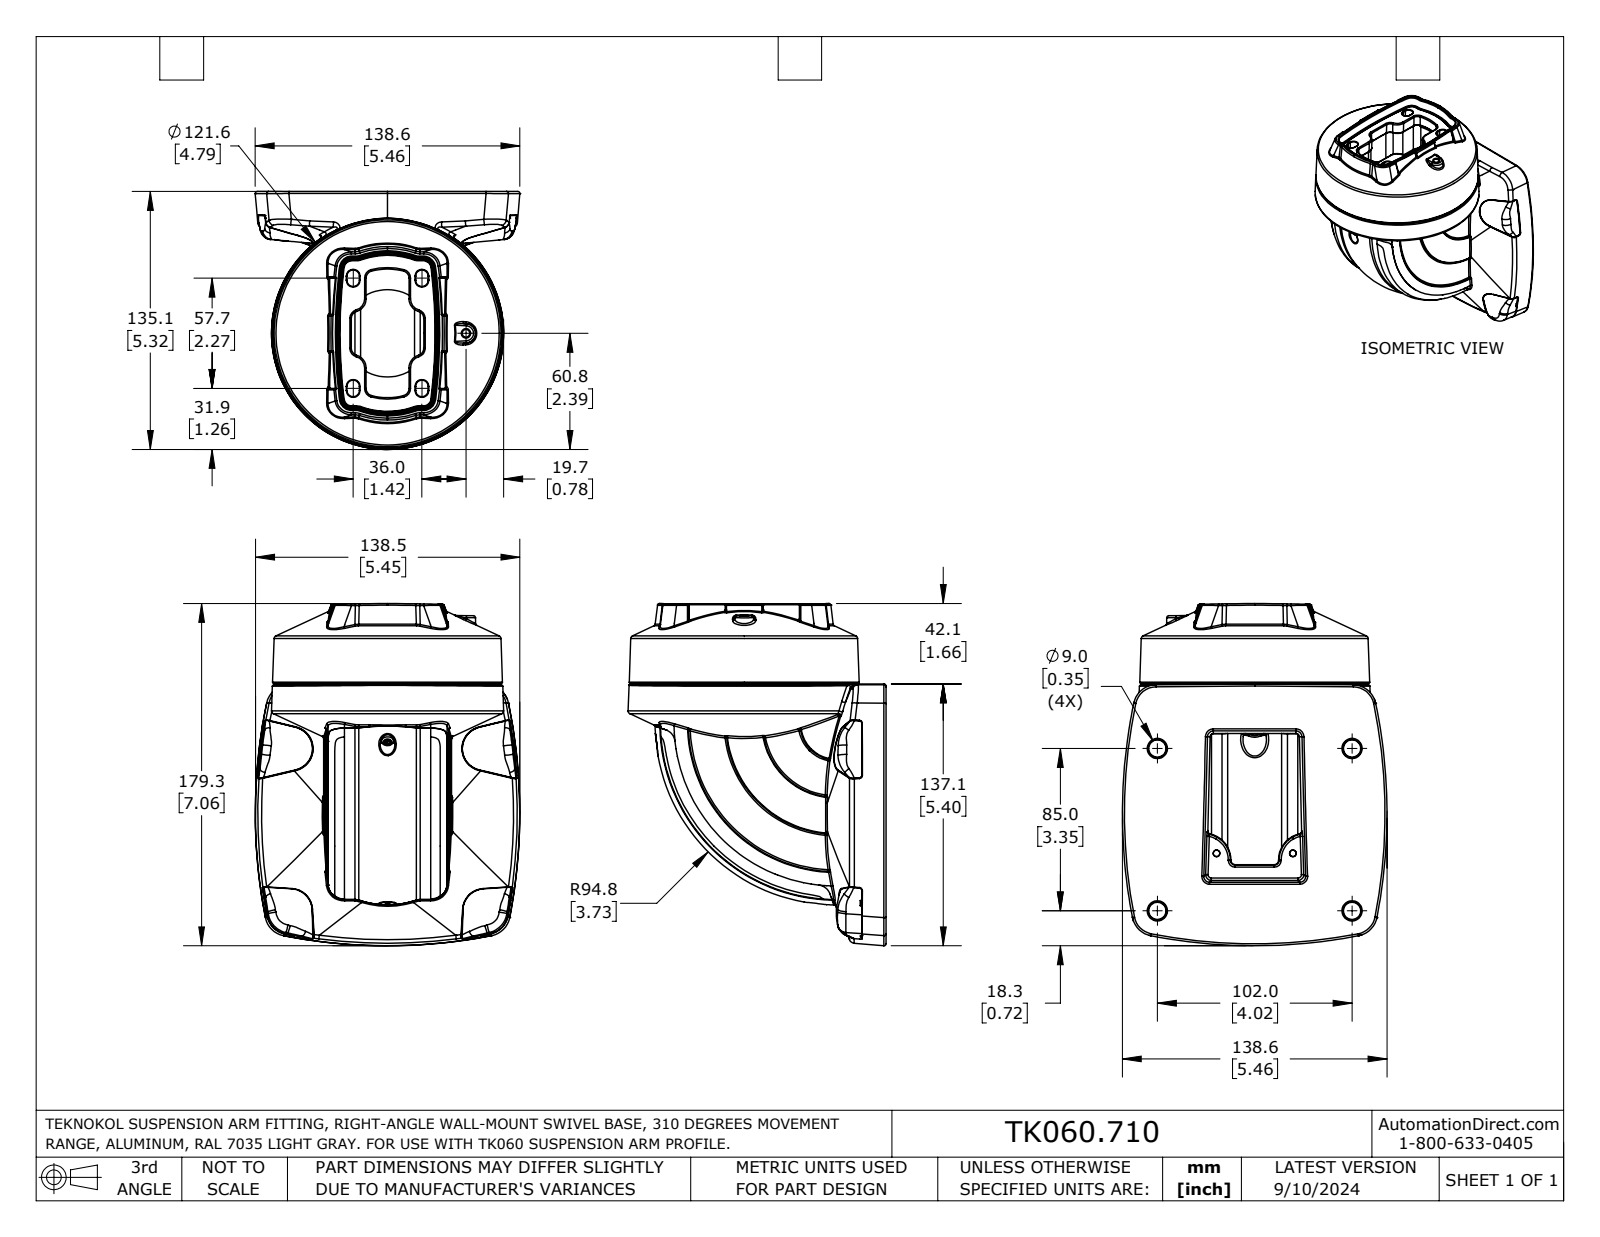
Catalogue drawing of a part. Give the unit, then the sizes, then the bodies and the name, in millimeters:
Units: millimetres
Overall size (bounding box): 179.3 × 138.6 × 135.1
Round holes (diameter × count): ⌀4.7 ×8, ⌀6.9 ×5, ⌀3.1 ×2, ⌀4 ×1, ⌀6.7 ×1, ⌀45.8 ×1
Round bosses / shafts (diameter × count): ⌀3.5 ×4, ⌀114.4 ×1, ⌀17.2 ×1, ⌀14.8 ×1, ⌀4.3 ×1, ⌀4.3 ×1
Partial cylindrical surfaces — rounded edges, fillets, slot ends (radius × count): R0.2 ×12, R2.4 ×12, R1.4 ×8, R3.6 ×8, R4.6 ×8, R1.6 ×7, R0.4 ×6, R3.2 ×6
Main face-to-face distances: 3, 46.4, 43.4, 19.7, 16.7, 26.7, 10.9, 11.4, 0.5, 49.4
Hole centre spacings: 37, 58.2, 39, 51, 72.1, 73.5, 94.2, 23
Volume: 1 035 000 mm³ · Surface area: 187 000 mm²
Bodies: 3 solids, 1568 faces (225 planar, 164 cylindrical, 1179 other)
Part name (STEP PRODUCT): TK060.710_REV1
STEP written by: SolidWorks 2023 (AUTOMOTIVE_DESIGN)
